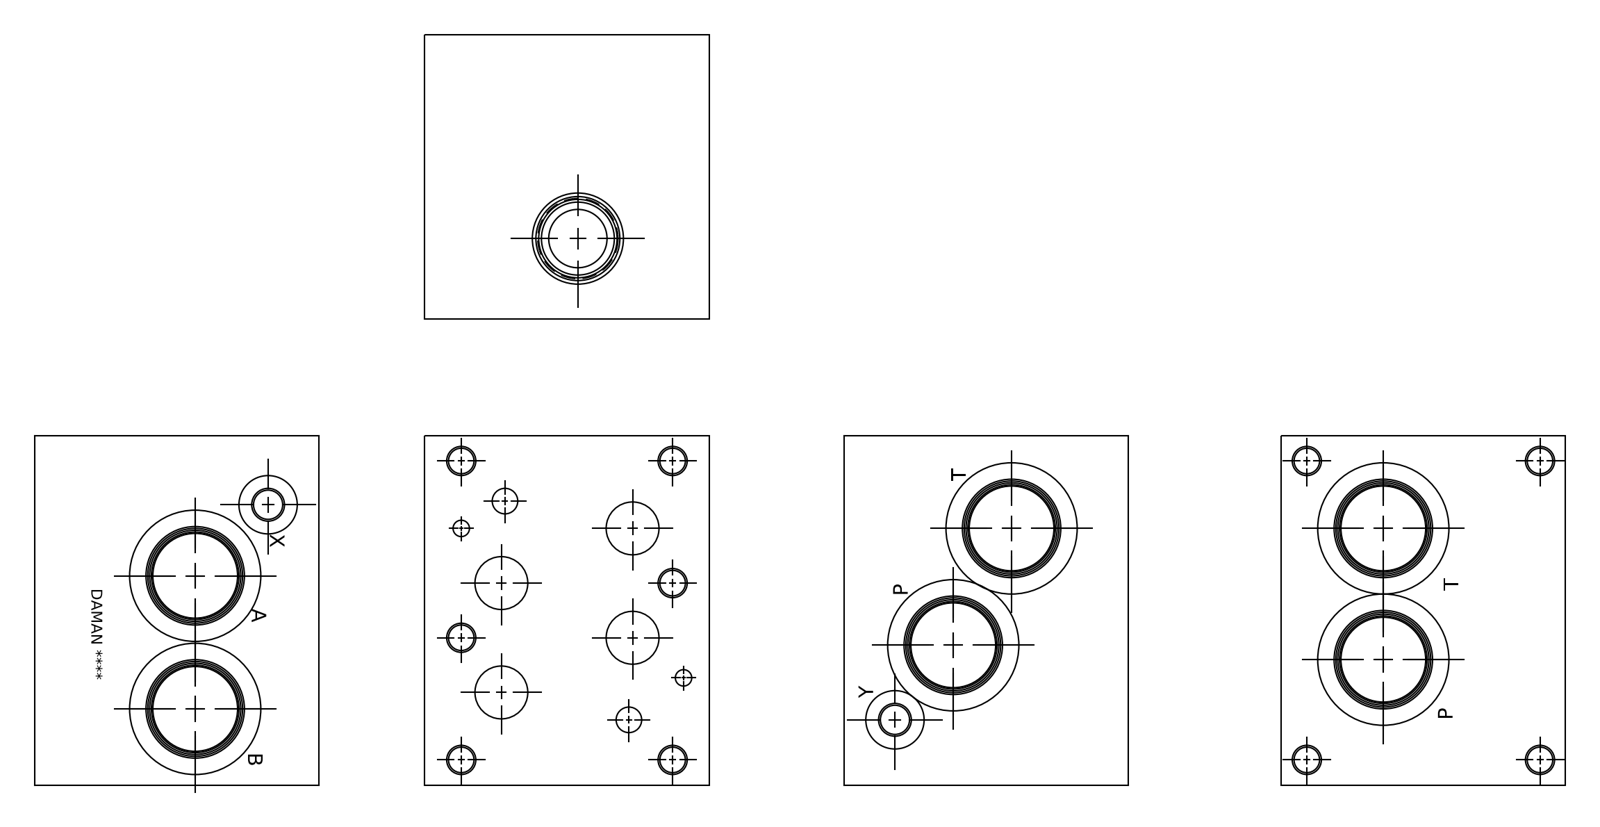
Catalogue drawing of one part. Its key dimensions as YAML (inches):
part_name: "Part_AD08SPRVS20S_3D"
step_written_by: "Autodesk Inventor 2019 (AUTOMOTIVE_DESIGN)"
units: inches
bodies: {solids: 1, faces: 632, planar: 336, cylindrical: 76, other: 220}
overall_size: [6, 4.875, 4.875]
volume: 114.3
surface_area: 251
round_holes:
  - {diameter: 0.422, count: 12}
  - {diameter: 0.5, count: 10}
  - {diameter: 1.5, count: 6}
  - {diameter: 1.544, count: 6}
  - {diameter: 2.306, count: 6}
  - {diameter: 0.969, count: 4}
  - {diameter: 1.625, count: 4}
  - {diameter: 1.644, count: 4}
  - {diameter: 0.281, count: 2}
  - {diameter: 0.484, count: 2}
  - {diameter: 0.508, count: 2}
  - {diameter: 0.562, count: 2}
partial_cylinders:
  - {radius: 0.453, count: 1}
face_to_face_distances: [4.875, 6, 0.031, 4.844, 4.813, 0.16, 4.715, 0.75, 0.781, 4.094]
hole_center_spacings: [1.163, 0.187, 1.017, 1.162, 1.875, 2.094, 2.237, 2.438]
